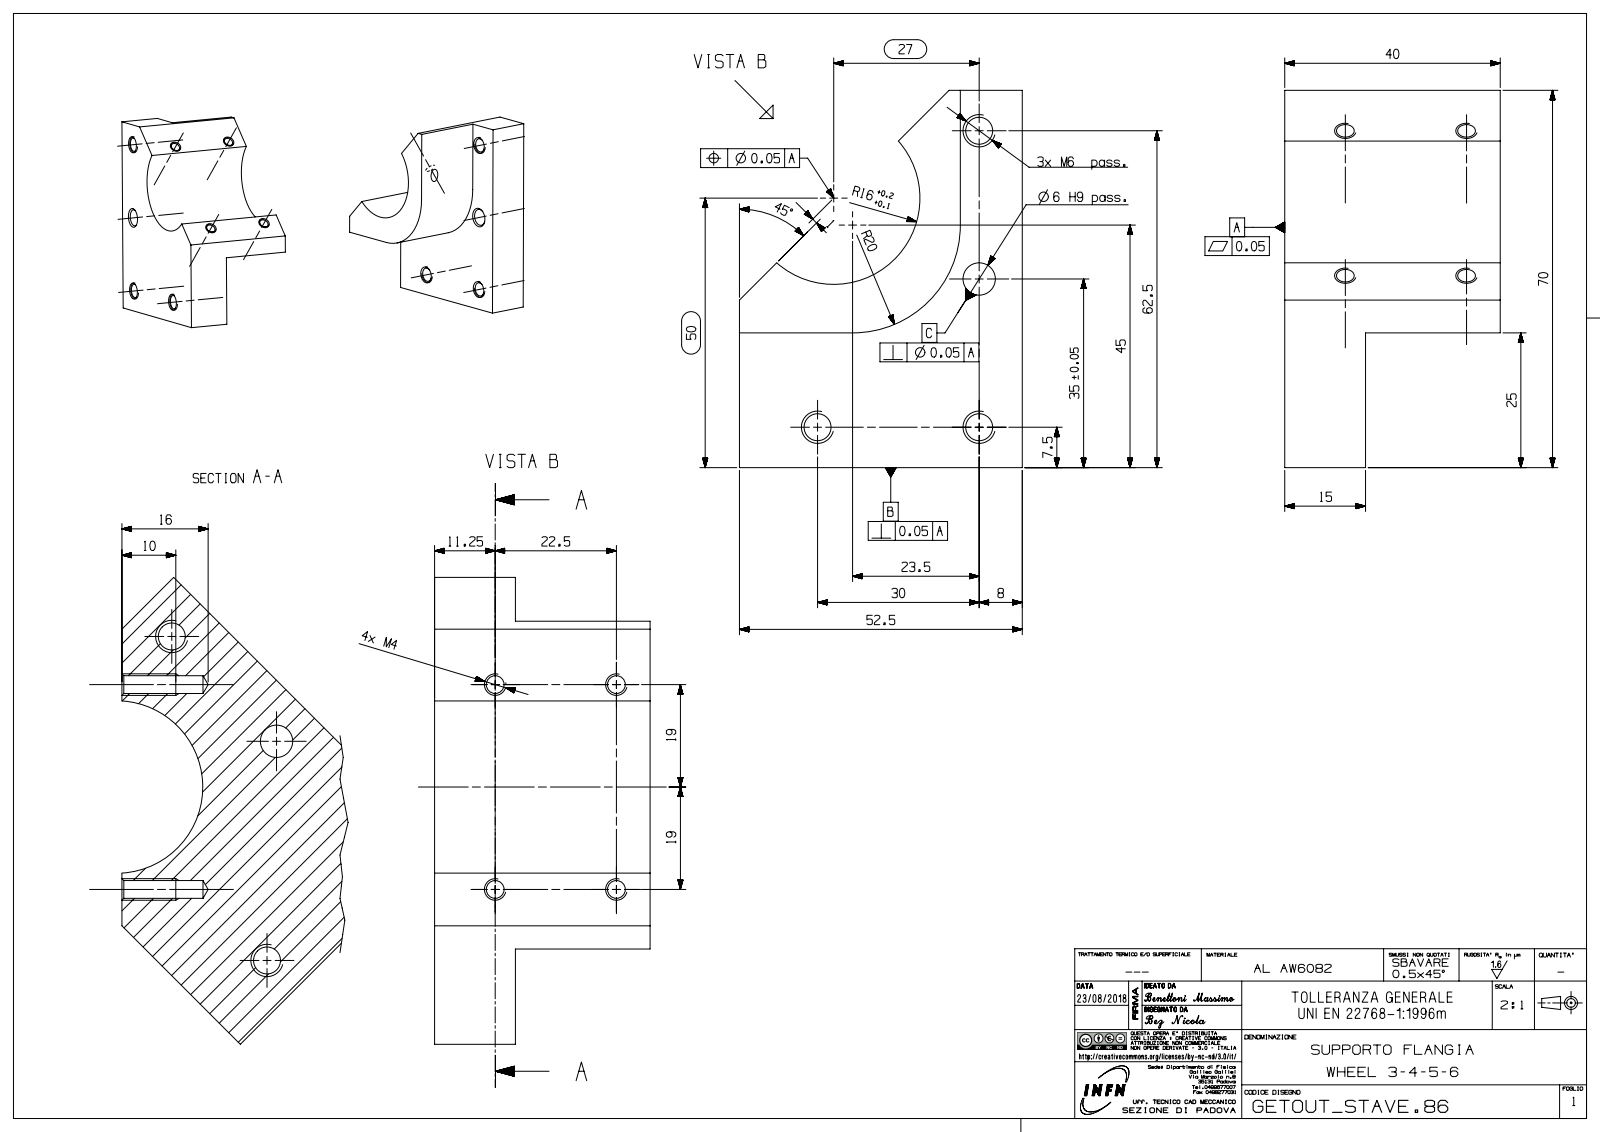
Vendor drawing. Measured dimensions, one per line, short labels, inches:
name: bez8324385A6uwo
written by: SIEMENS PLM Software NX 12.0 (AUTOMOTIVE_DESIGN)
unit: in
bodies: 1 solid, 35 faces (11 planar, 10 cylindrical, 14 other)
size: 2.756 × 2.067 × 1.575
volume: 3.184 in³; area: 21.6 in²
holes: 4× ⌀0.13, 3× ⌀0.197, 1× ⌀0.236
rounds: 1× R0.63, 1× R0.787
face distances: 0.591, 0.984, 1.575, 2.067, 0.453, 1.614, 1.772, 2.756
hole spacings: 0.886, 1.083, 1.496, 1.739, 1.181, 1.602, 2.165, 2.467
